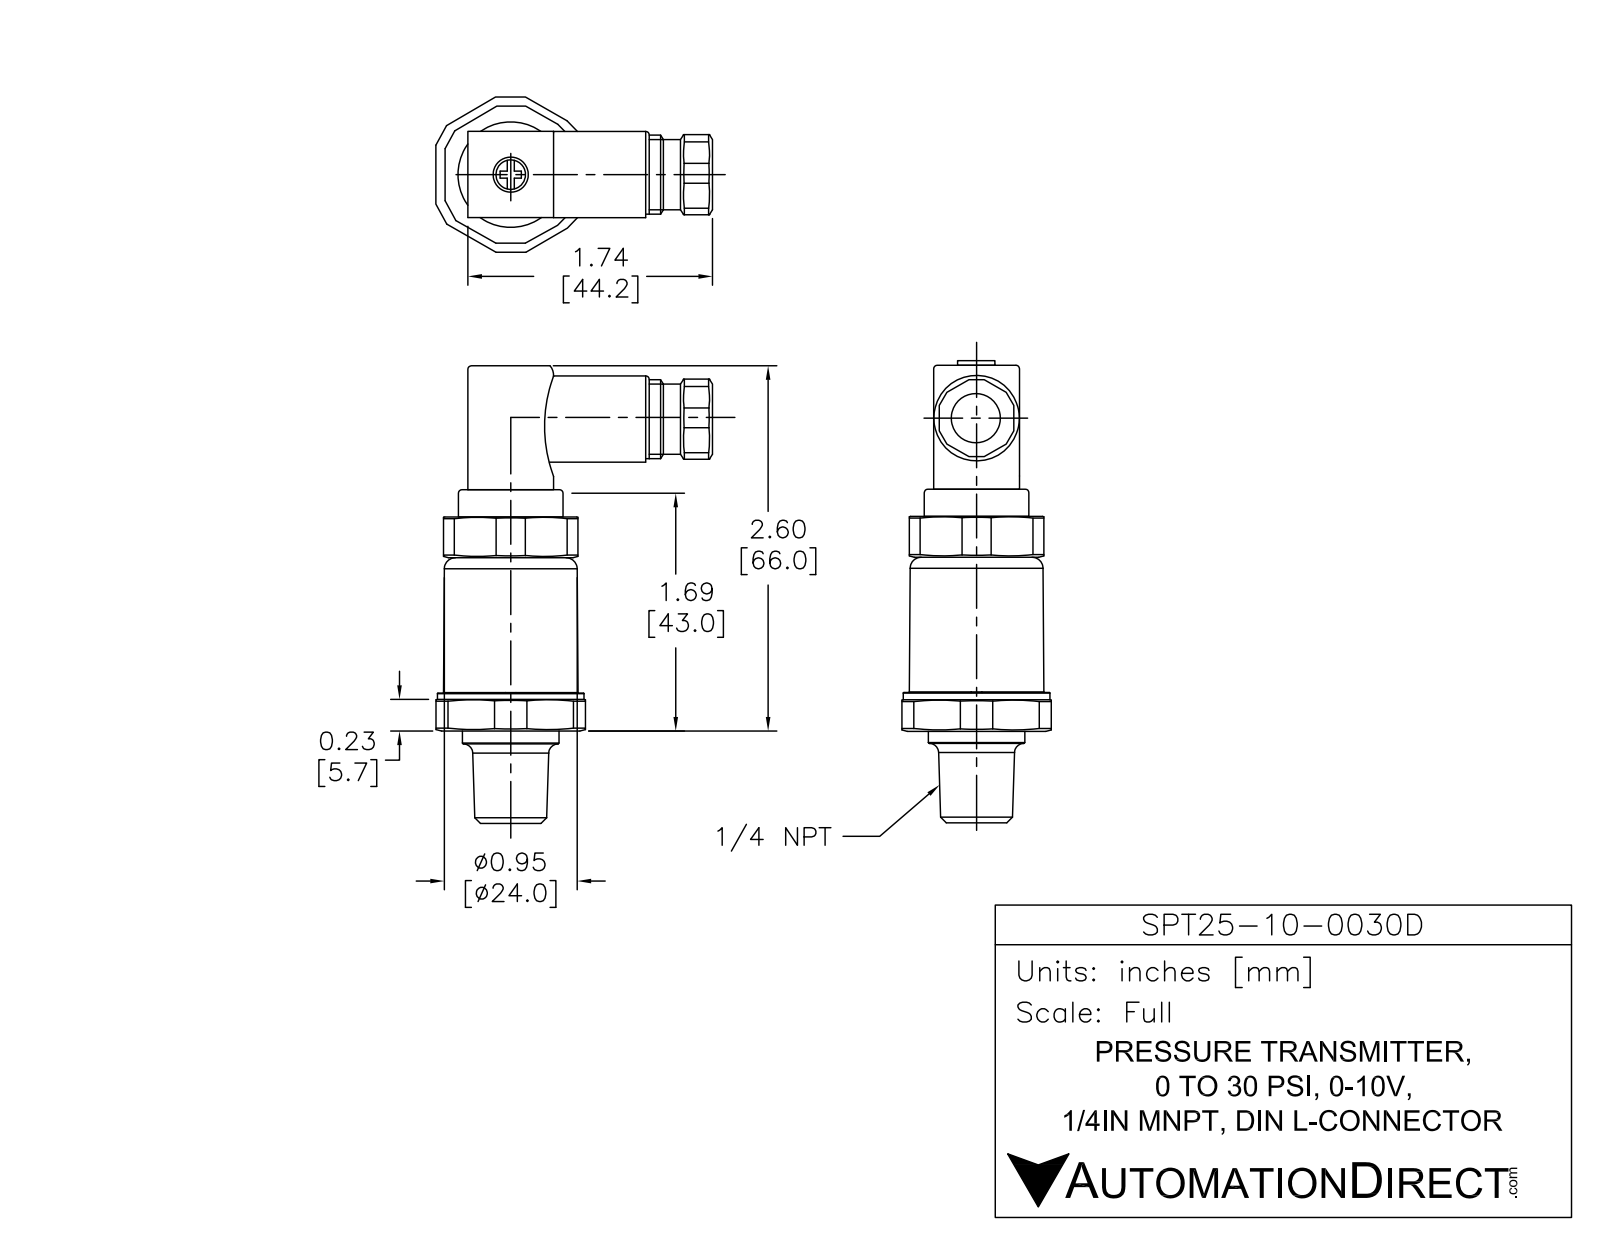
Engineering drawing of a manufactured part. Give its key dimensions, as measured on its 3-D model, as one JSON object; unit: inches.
{"part_name": "SPT25-10-0030D", "step_written_by": "SolidWorks 2013 (AUTOMOTIVE_DESIGN)", "units": "inches", "bodies": {"solids": 5, "faces": 200, "planar": 96, "cylindrical": 87, "other": 17}, "overall_size": [3.199, 1.496, 1.406], "volume_in3": 1.702, "surface_area_in2": 15.71, "round_holes": [[0.039, 1], [0.13, 1], [0.276, 1], [0.315, 1]], "round_bosses_or_shafts": [[1.053, 1], [0.945, 1], [0.689, 1], [0.591, 1], [0.551, 1], [0.433, 1]], "partial_cylinders_radius": [[0.059, 8], [0.045, 4], [0.089, 4], [0.079, 3], [0.045, 1], [0.046, 1], [0.571, 1]], "face_to_face_distances": [0.059, 1.161, 1.22, 0.62, 0.014, 0.606, 0.266, 1.486, 1.427, 0.197], "hole_center_spacings": [0.052]}
